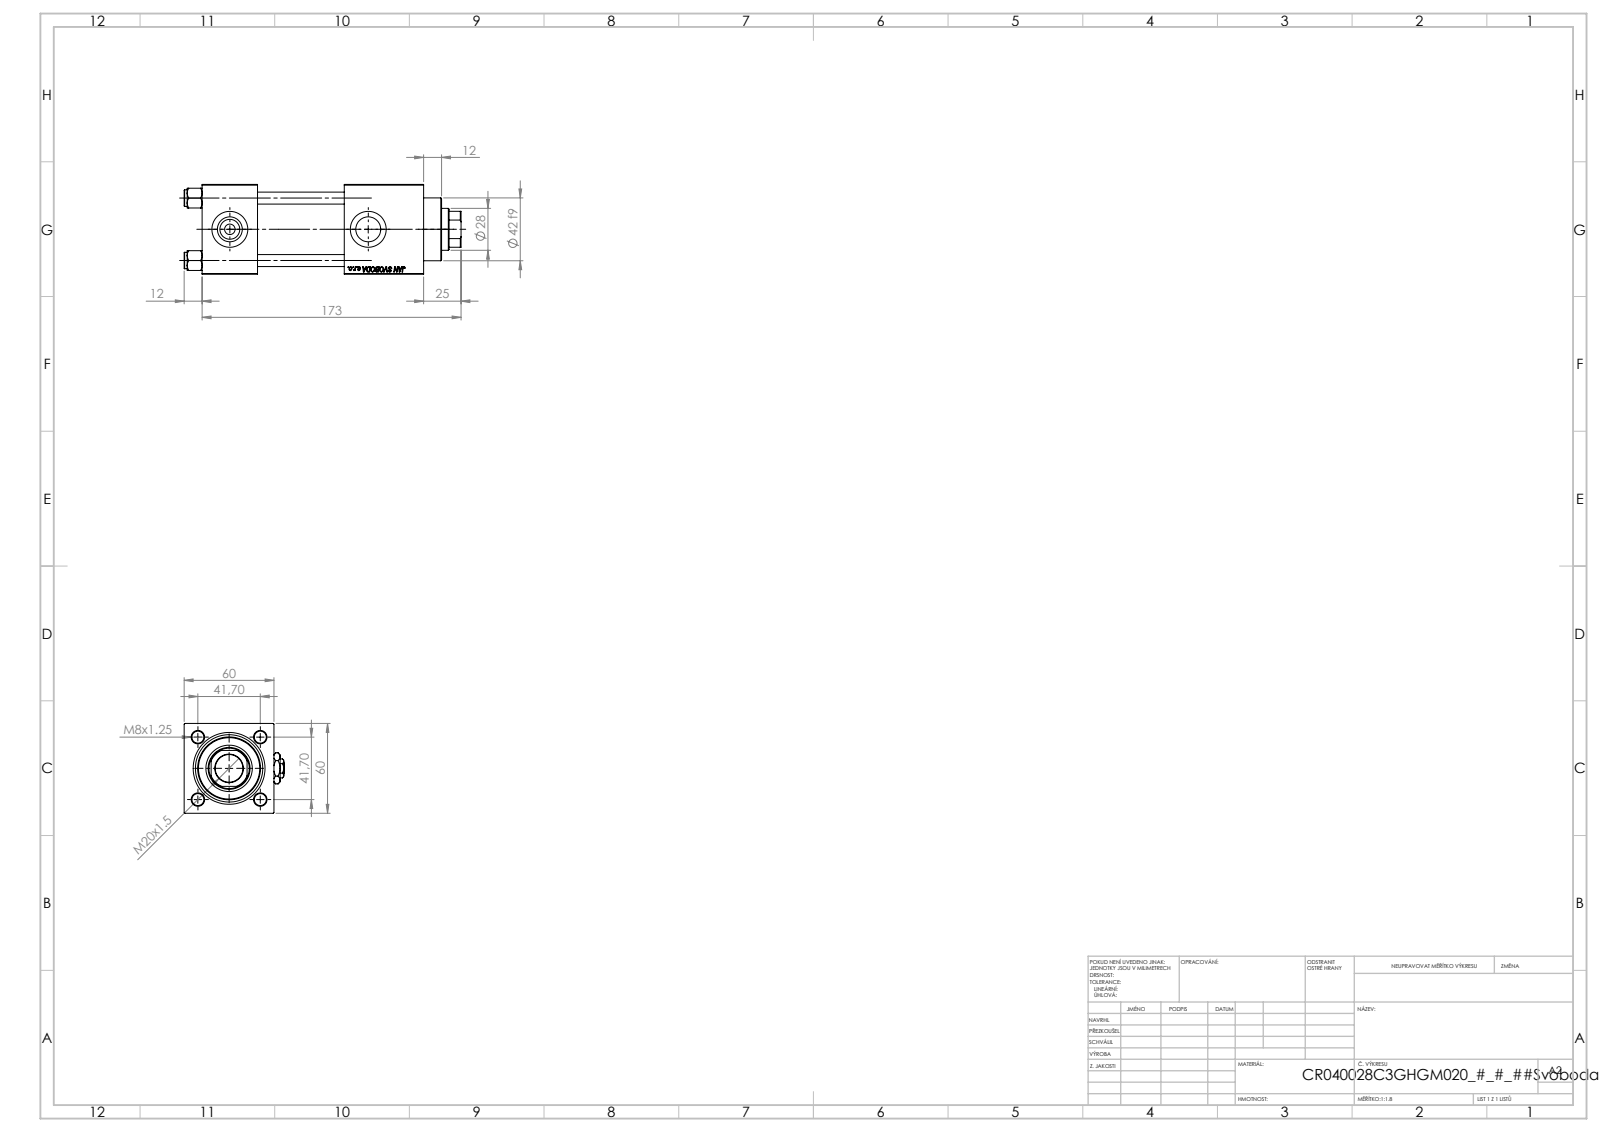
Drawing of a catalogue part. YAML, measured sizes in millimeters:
part_name: "V215CR_VCP_C; V215CR_C_TYCINKA; V215_VC_A; V215CR_C_Body (+2 more)"
step_written_by: "SolidWorks 2019 (CONFIG_CONTROL_DESIGN)"
units: millimeters
bodies: {solids: 13, faces: 1250, planar: 574, cylindrical: 98, other: 578}
overall_size: [185, 67, 60]
volume: 420937
surface_area: 114350
round_holes:
  - {diameter: 8, count: 4}
  - {diameter: 7, count: 2}
  - {diameter: 16.66, count: 2}
  - {diameter: 24, count: 2}
  - {diameter: 18.5, count: 1}
  - {diameter: 28, count: 1}
  - {diameter: 31, count: 1}
  - {diameter: 40, count: 1}
  - {diameter: 45, count: 1}
round_bosses_or_shafts:
  - {diameter: 11, count: 4}
  - {diameter: 46, count: 1}
  - {diameter: 42, count: 1}
partial_cylinders:
  - {radius: 13.5, count: 1}
face_to_face_distances: [60, 37, 58, 95, 53, 119.3, 82.3, 24.3, 148, 111]
hole_center_spacings: [29.49, 41.7, 58.97, 92.5]
